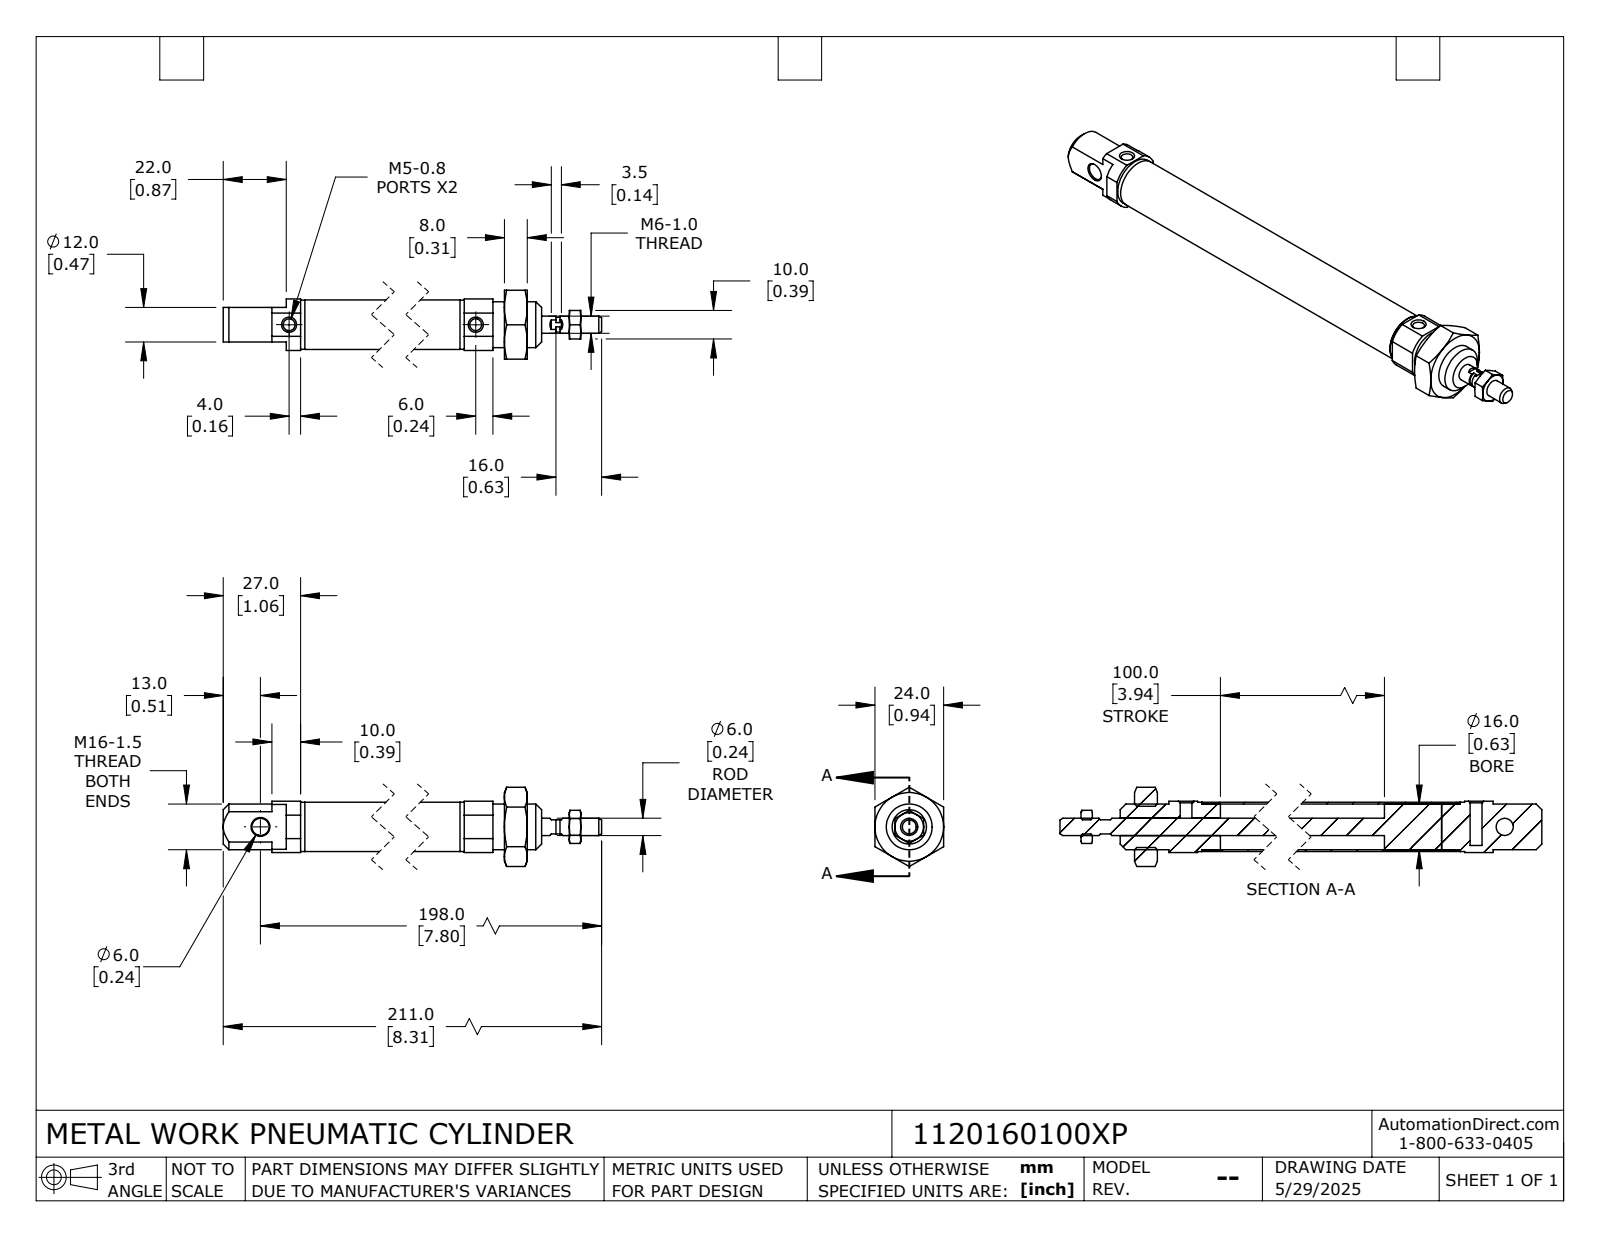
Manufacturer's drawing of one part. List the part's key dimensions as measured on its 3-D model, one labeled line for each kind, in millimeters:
Part name (STEP PRODUCT): 1120160100XP_BODY; 1120160100XP; 1120160100XP_ROD
STEP written by: SolidWorks 2024 (CONFIG_CONTROL_DESIGN)
Units: millimetres
Bodies: 6 solids, 146 faces (55 planar, 45 cylindrical, 46 other)
Overall size (bounding box): 211 × 27.71 × 24
Volume: 28 997 mm³ · Surface area: 25 998 mm²
Round holes (diameter × count): ⌀4.13 ×2, ⌀4.92 ×1, ⌀6 ×1, ⌀14.38 ×1
Round bosses / shafts (diameter × count): ⌀17.27 ×1, ⌀17.2 ×1, ⌀16.15 ×1, ⌀16 ×1, ⌀6 ×1, ⌀5.2 ×1
Partial cylindrical surfaces — rounded edges, fillets, slot ends (radius × count): R9.85 ×1
Main face-to-face distances: 8, 18, 24, 22, 150, 12, 155, 17, 142, 2.97
Hole centre spacings: 144
